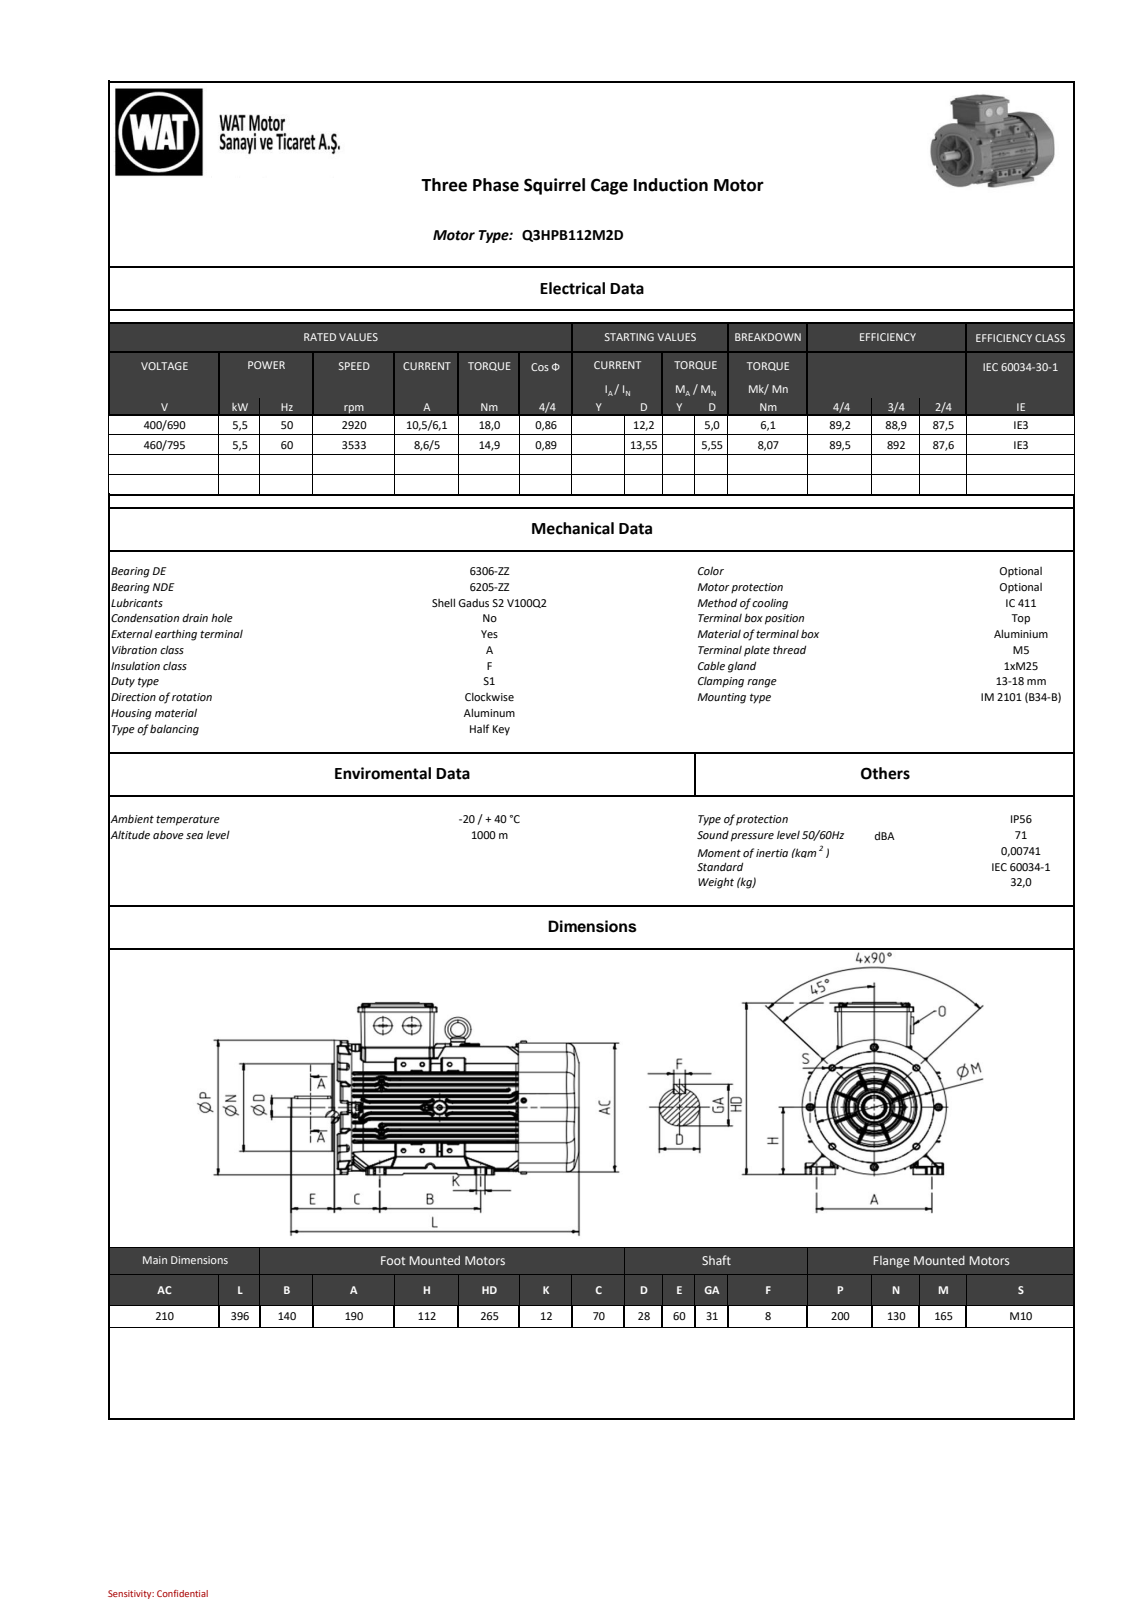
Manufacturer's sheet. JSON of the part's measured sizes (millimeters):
{"part_name": "QH series_ 112_B34b_stp_objects", "step_written_by": "SIEMENS PLM Software NX2206.8101 (AUTOMOTIVE_DESIGN)", "units": "millimeters", "bodies": {"solids": 0, "faces": 6957, "planar": 1594, "cylindrical": 2650, "other": 2713}, "overall_size": [396, 274.5, 225.11], "round_holes": [[4.6, 2], [8, 1], [8.5, 1]], "round_bosses_or_shafts": [[13, 4], [10, 4], [8, 4], [14.8, 3], [25, 2], [6, 2], [188, 1], [130, 1]], "partial_cylinders_radius": [[2, 599], [0.8, 571], [1, 321], [0.5, 282], [3, 63], [4, 12], [6, 12], [10, 10]], "face_to_face_distances": [1, 21.5, 10.99, 35.96, 99.54, 24.97, 8.16, 112.88, 89.87, 90.43]}
